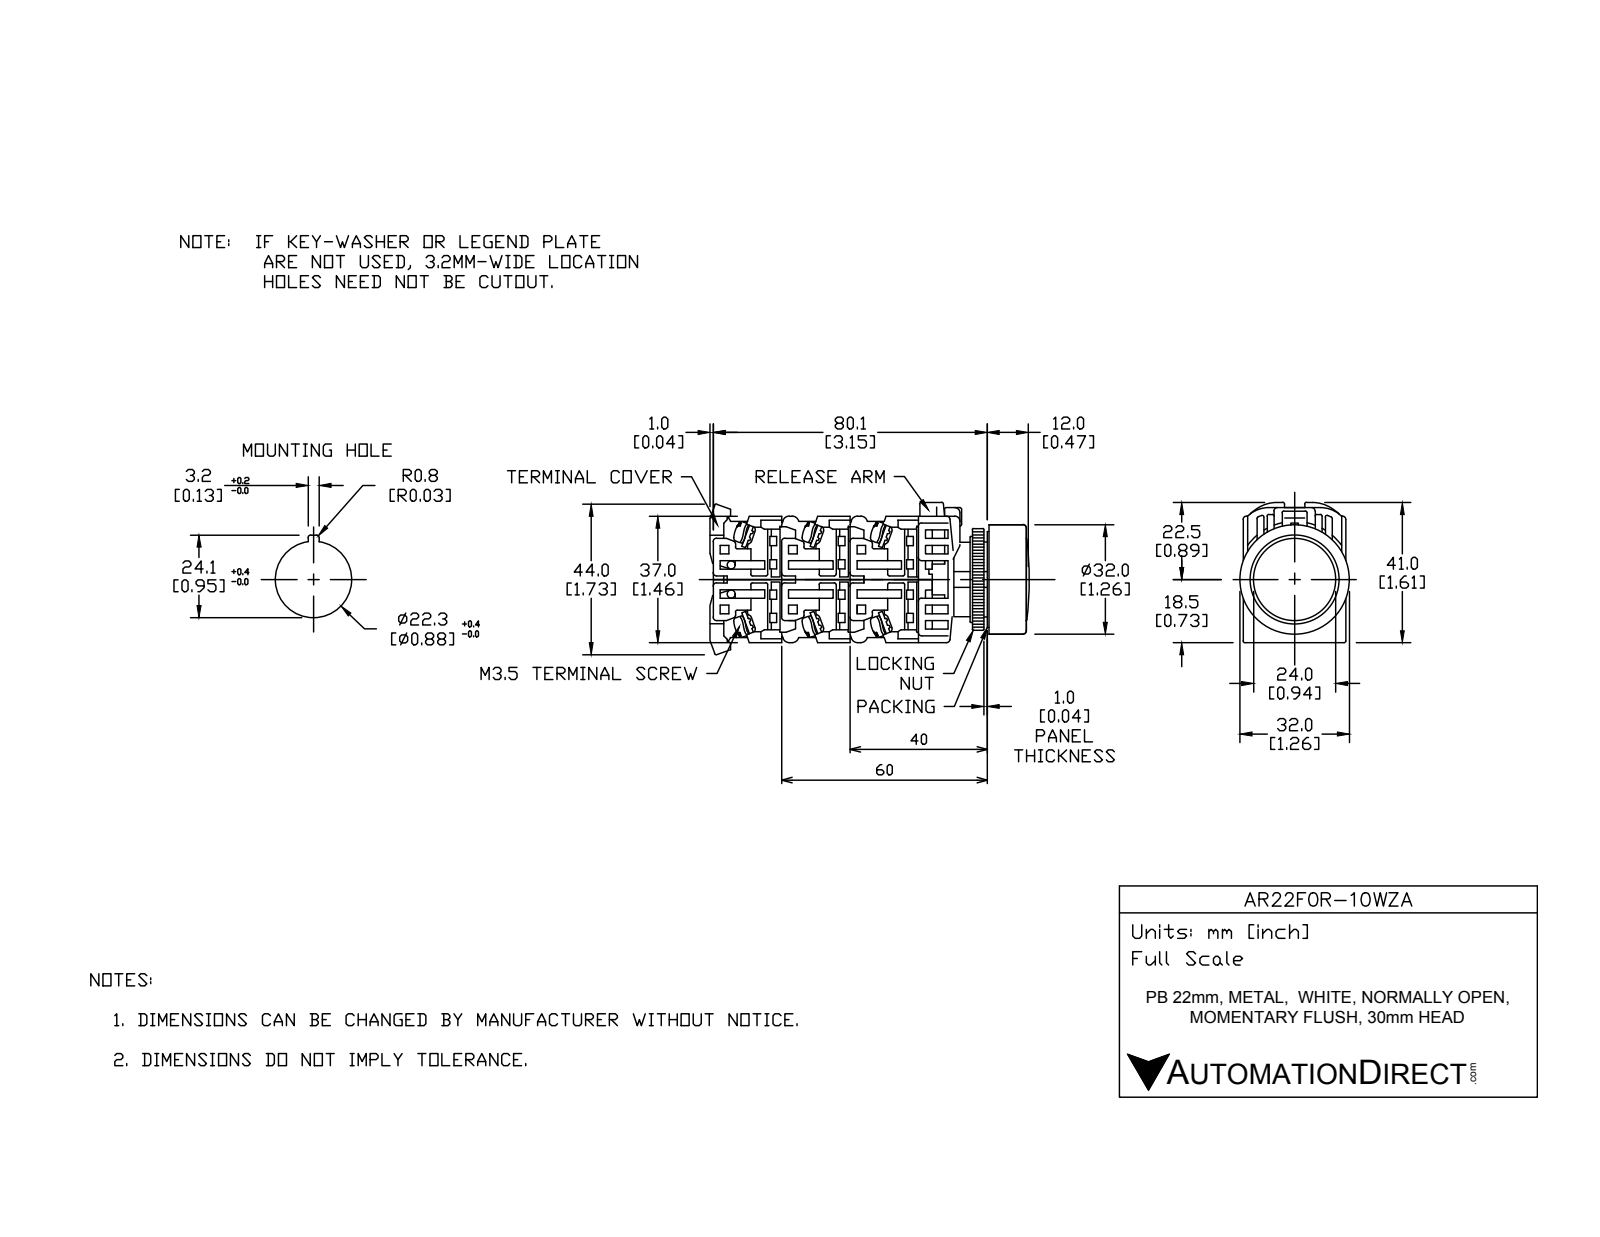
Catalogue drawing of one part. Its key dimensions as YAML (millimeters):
part_name: "AR22F0R-10WZA"
step_written_by: "SolidWorks 2017 (AUTOMOTIVE_DESIGN)"
units: millimeters
bodies: {solids: 12, faces: 295, planar: 201, cylindrical: 74, other: 20}
overall_size: [52.75, 41, 32]
volume: 27343
surface_area: 19391
round_holes:
  - {diameter: 21.8, count: 1}
  - {diameter: 22, count: 1}
  - {diameter: 25, count: 1}
  - {diameter: 31, count: 1}
round_bosses_or_shafts:
  - {diameter: 5, count: 2}
  - {diameter: 32, count: 1}
  - {diameter: 30.5, count: 1}
  - {diameter: 29.8, count: 1}
  - {diameter: 24, count: 1}
  - {diameter: 23.8, count: 1}
  - {diameter: 21.75, count: 1}
  - {diameter: 17, count: 1}
partial_cylinders:
  - {radius: 0.5, count: 23}
  - {radius: 1.75, count: 4}
  - {radius: 5, count: 4}
  - {radius: 4, count: 2}
  - {radius: 16.59, count: 1}
  - {radius: 17.59, count: 1}
face_to_face_distances: [1, 28.5, 18, 3, 2, 29, 30, 10.5, 8, 20.5]
